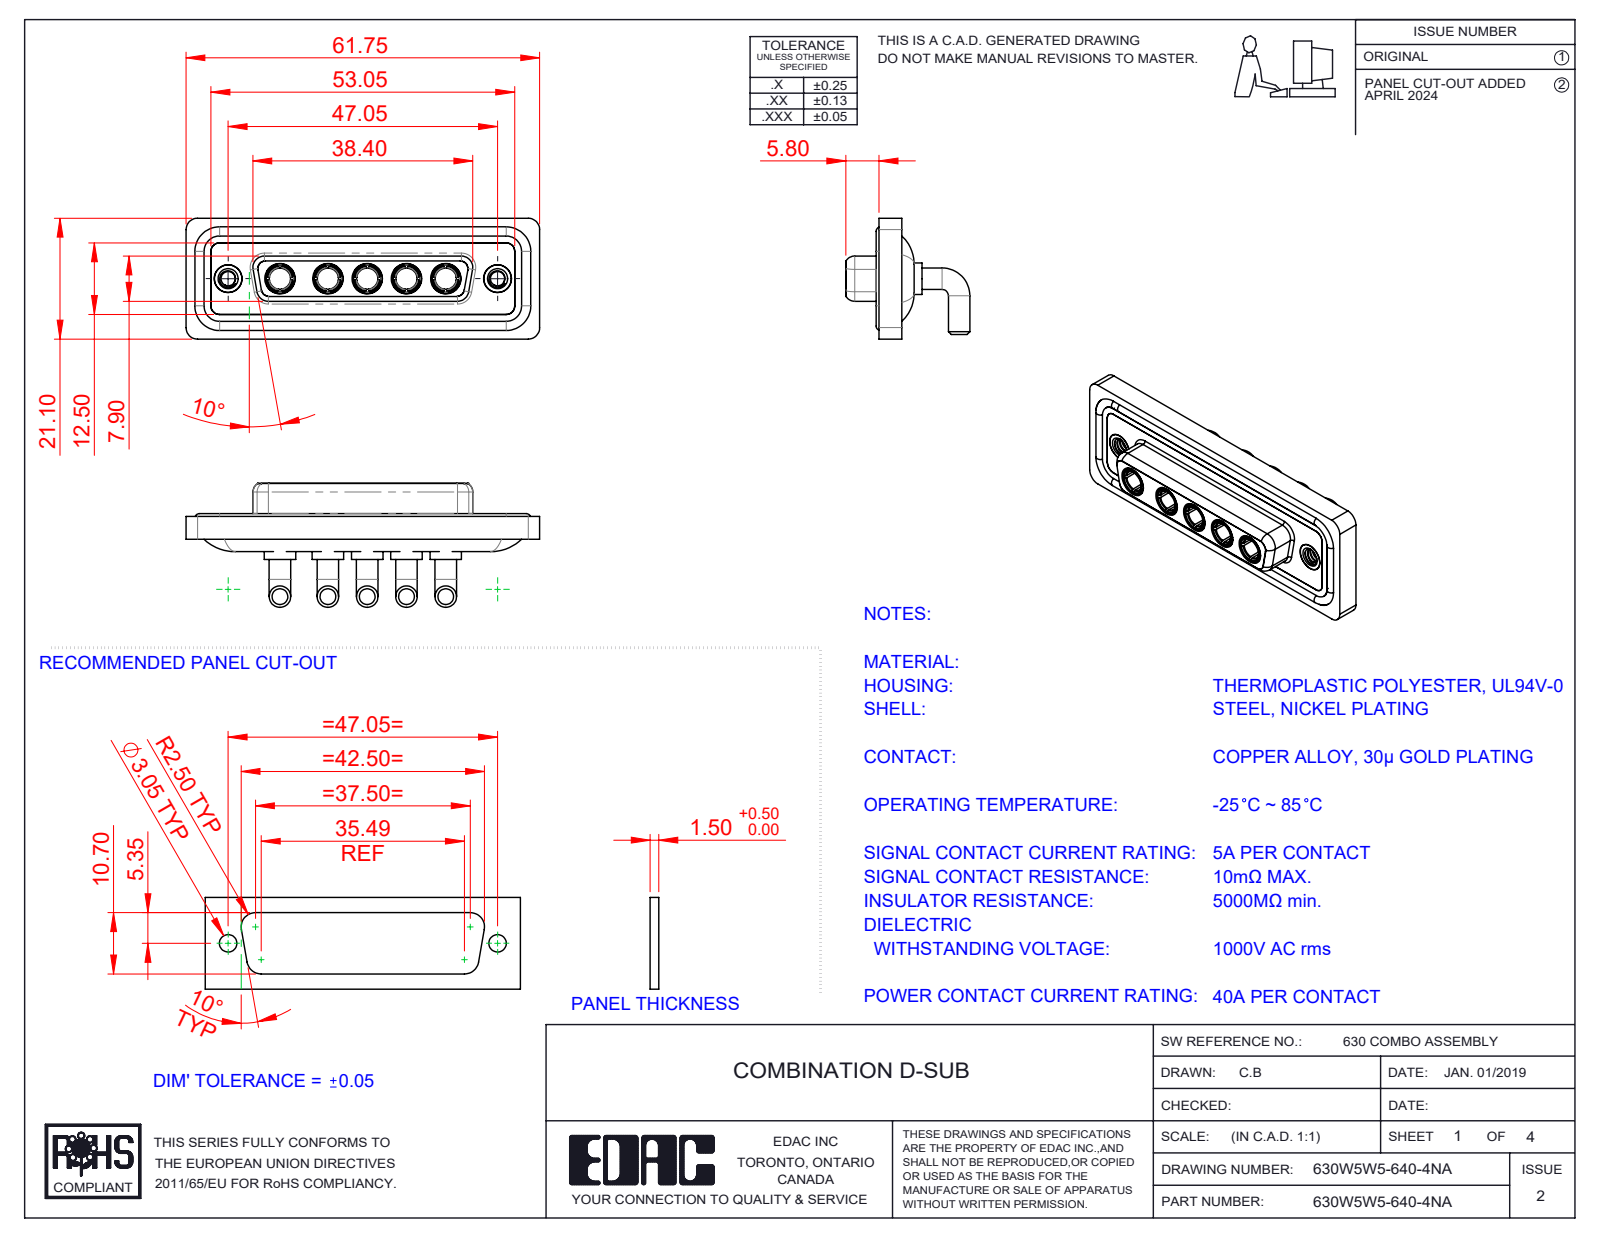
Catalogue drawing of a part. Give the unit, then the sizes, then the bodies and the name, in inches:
Units: inches
Overall size (bounding box): 2.431 × 0.854 × 0.831
Round holes (diameter × count): ⌀0.191 ×7, ⌀0.146 ×5, ⌀0.209 ×5, ⌀0.098 ×2, ⌀0.157 ×2, ⌀0.159 ×2, ⌀0.197 ×2
Round bosses / shafts (diameter × count): ⌀0.148 ×10, ⌀0.217 ×5, ⌀0.205 ×5, ⌀0.195 ×5, ⌀0.187 ×5, ⌀0.063 ×4, ⌀0.195 ×2, ⌀0.189 ×2
Partial cylindrical surfaces — rounded edges, fillets, slot ends (radius × count): R0.059 ×18, R0.079 ×18, R0.053 ×8, R0.063 ×8, R0.083 ×5, R0.01 ×4, R0.02 ×4, R0.024 ×4
Main face-to-face distances: 0.016, 0.071, 0.161, 0.043, 0.098, 0.122, 0.146, 0.063, 0.059, 0.114
Hole centre spacings: 0.27, 0.356, 1.496, 0.27, 0.33, 0.54, 0.541, 0.6
Volume: 0.536 in³ · Surface area: 21.75 in²
Bodies: 17 solids, 770 faces (250 planar, 311 cylindrical, 209 other)
Part name (STEP PRODUCT): 630Combo Threaded Rivet_A; 630Combo Shell Front_25 Contacts; 630W5W5-640-4NA; 630Combo Housing_5W5 (+3 more)
STEP written by: SolidWorks 2023 (CONFIG_CONTROL_DESIGN)
